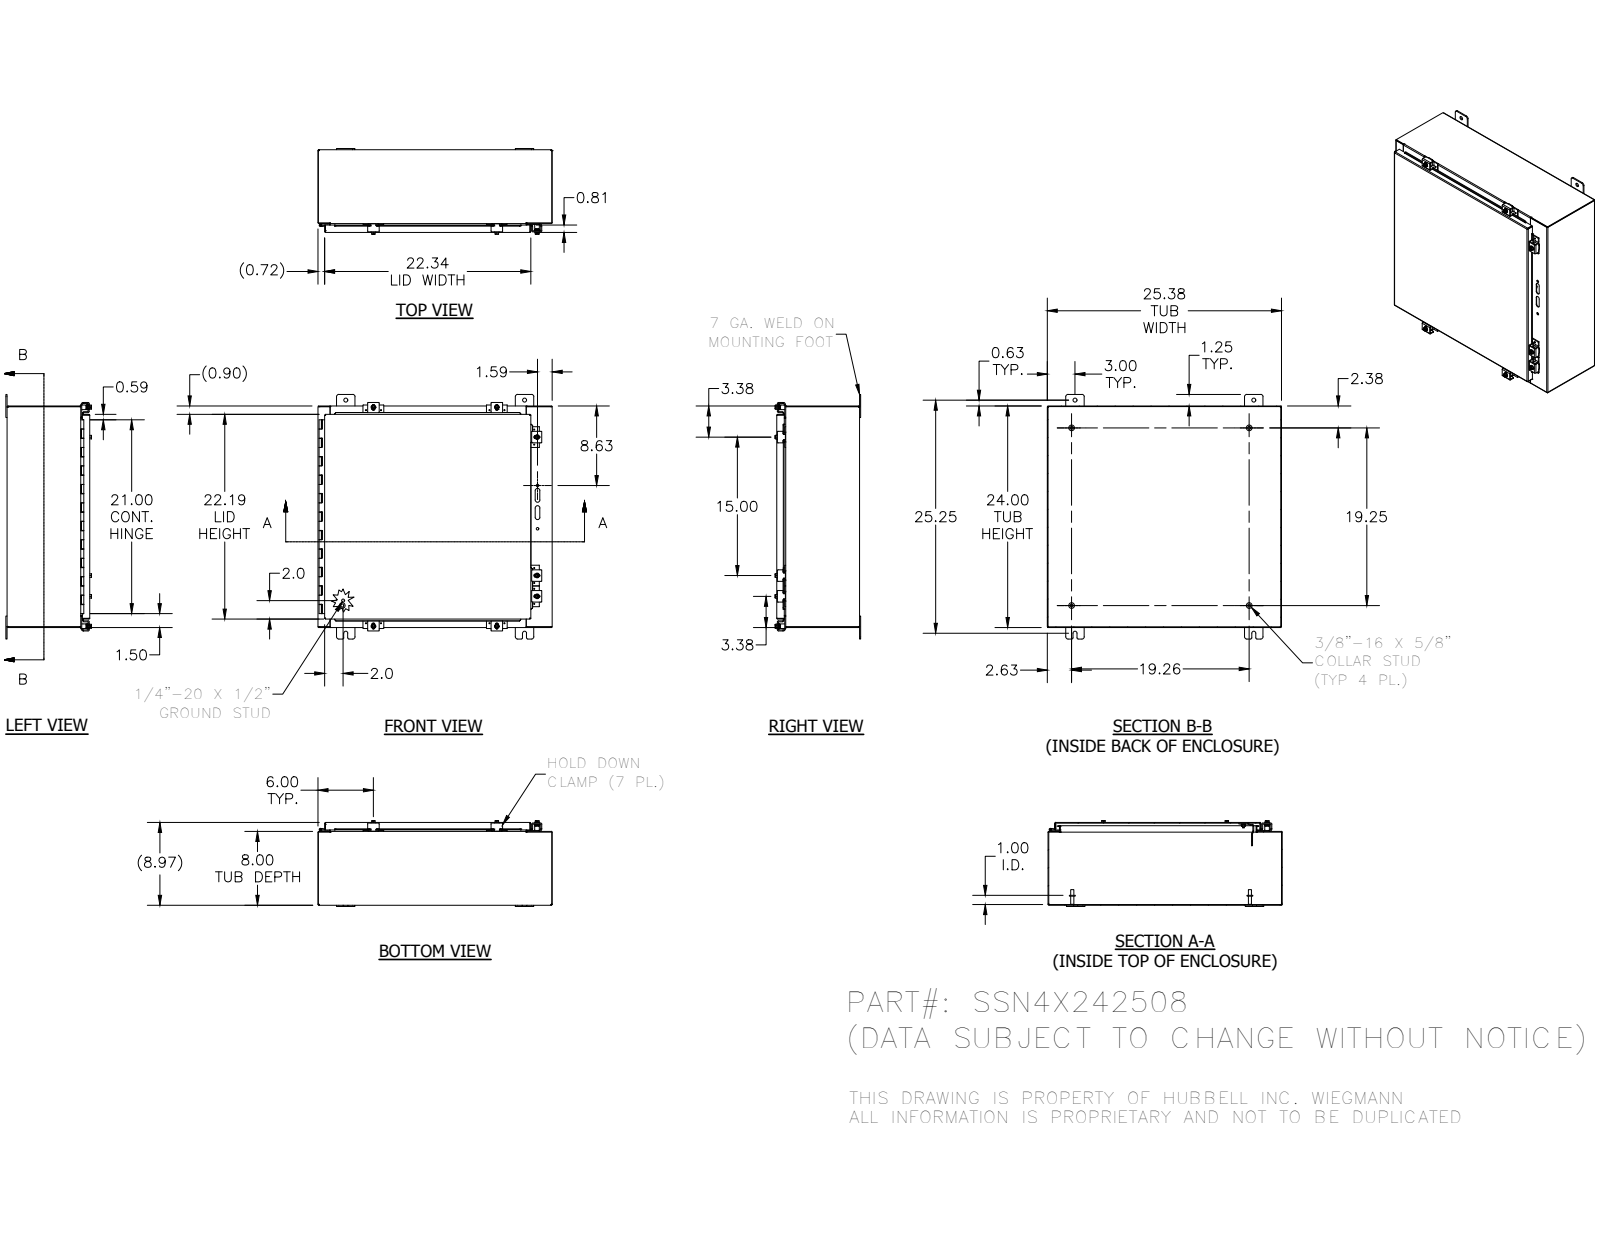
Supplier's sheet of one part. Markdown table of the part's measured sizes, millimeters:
| quantity | value |
| --- | --- |
| part name | SSN4X242508; SSN4X242508BKP; 38859; 34871 (+8 more) |
| STEP written by | Autodesk Inventor 2012 (AUTOMOTIVE_DESIGN) |
| units | millimeters |
| bodies | 54 solids, 1564 faces (844 planar, 497 cylindrical, 223 other) |
| overall size | 673.1 × 644.7 × 235.5 |
| volume | 2 792 000 mm³ |
| surface area | 2 977 000 mm² |
| round holes (diameter × count) | 2.8 × 14, 7.1 × 9, 5.4 × 7, 7.6 × 7, 11.1 × 4, 4 × 2, 3.2 × 1 |
| round bosses / shafts (diameter × count) | 6.4 × 11, 13.2 × 7, 12.7 × 7, 8.9 × 7, 15.9 × 4, 8.4 × 4, 4.8 × 2, 8.6 × 1 |
| partial cylindrical surfaces (radius × count) | 0.8 × 81, 6.4 × 33, 3.2 × 28, 0.8 × 23, 2.7 × 23, 1.6 × 17, 3.6 × 14, 2.5 × 10 |
| main face-to-face distances | 1.9, 226, 224.1, 227.9, 607.7, 642.8, 201.3, 24.7, 609.6, 605.8 |
| hole center spacings | 22.3, 595.1, 339.9, 41.3, 319.3, 360.6, 586.4, 587.8 |
